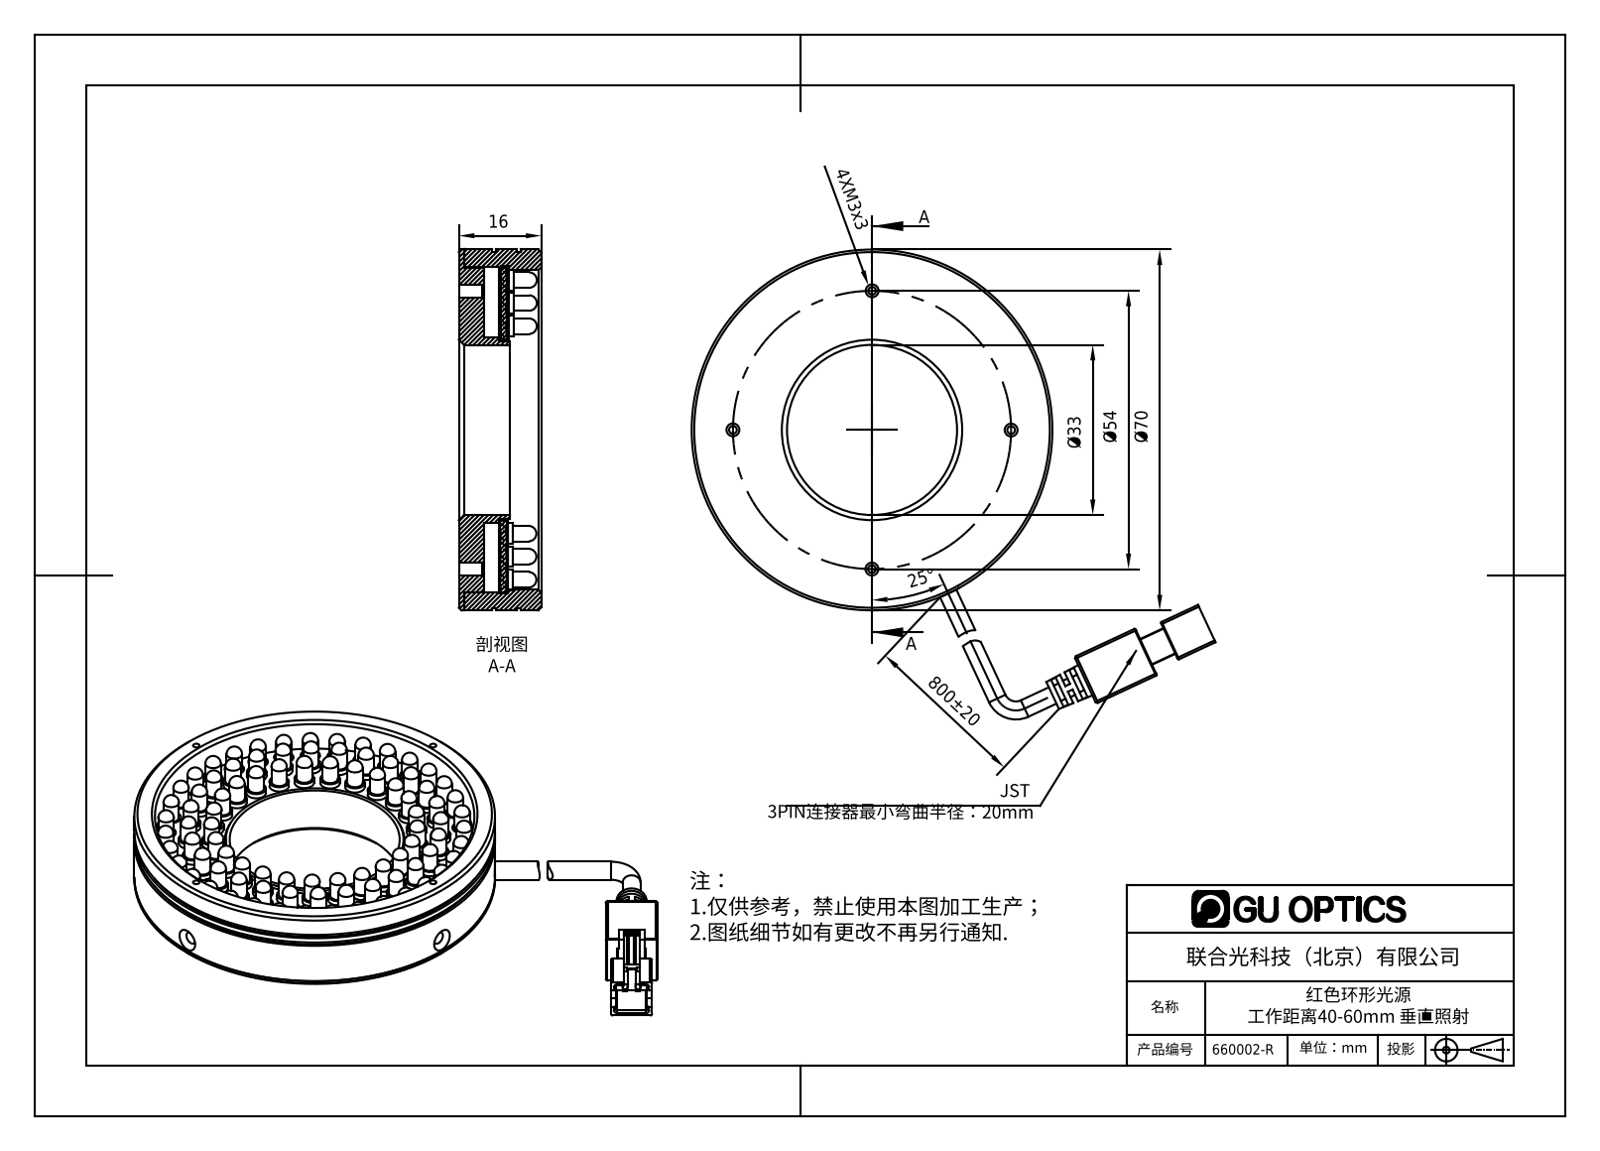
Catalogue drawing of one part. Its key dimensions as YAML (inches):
part_name: "660002-R"
step_written_by: "SolidWorks 2016 (AUTOMOTIVE_DESIGN)"
units: inches
bodies: {solids: 94, faces: 1870, planar: 1211, cylindrical: 501, other: 158}
overall_size: [4.398, 3.094, 0.728]
volume: 1.959
surface_area: 48.67
round_holes:
  - {diameter: 0.049, count: 4}
  - {diameter: 0.098, count: 4}
  - {diameter: 0.063, count: 2}
  - {diameter: 0.094, count: 2}
  - {diameter: 1.299, count: 1}
  - {diameter: 1.378, count: 1}
  - {diameter: 2.441, count: 1}
  - {diameter: 2.488, count: 1}
round_bosses_or_shafts:
  - {diameter: 0.15, count: 89}
  - {diameter: 0.118, count: 89}
  - {diameter: 0.138, count: 2}
  - {diameter: 2.756, count: 1}
  - {diameter: 2.717, count: 1}
  - {diameter: 2.48, count: 1}
  - {diameter: 1.413, count: 1}
  - {diameter: 1.358, count: 1}
partial_cylinders:
  - {radius: 0.004, count: 15}
  - {radius: 0.008, count: 13}
  - {radius: 0.016, count: 12}
  - {radius: 0.012, count: 1}
  - {radius: 0.027, count: 1}
  - {radius: 0.055, count: 1}
  - {radius: 0.069, count: 1}
  - {radius: 0.276, count: 1}
face_to_face_distances: [0.37, 0.039, 0.189, 0.063, 0.118, 0.307, 0.181, 0.331, 0.15, 0.268]
hole_center_spacings: [1.063, 1.28, 1.809, 2.307, 0.459, 1.356, 1.503, 1.922]
